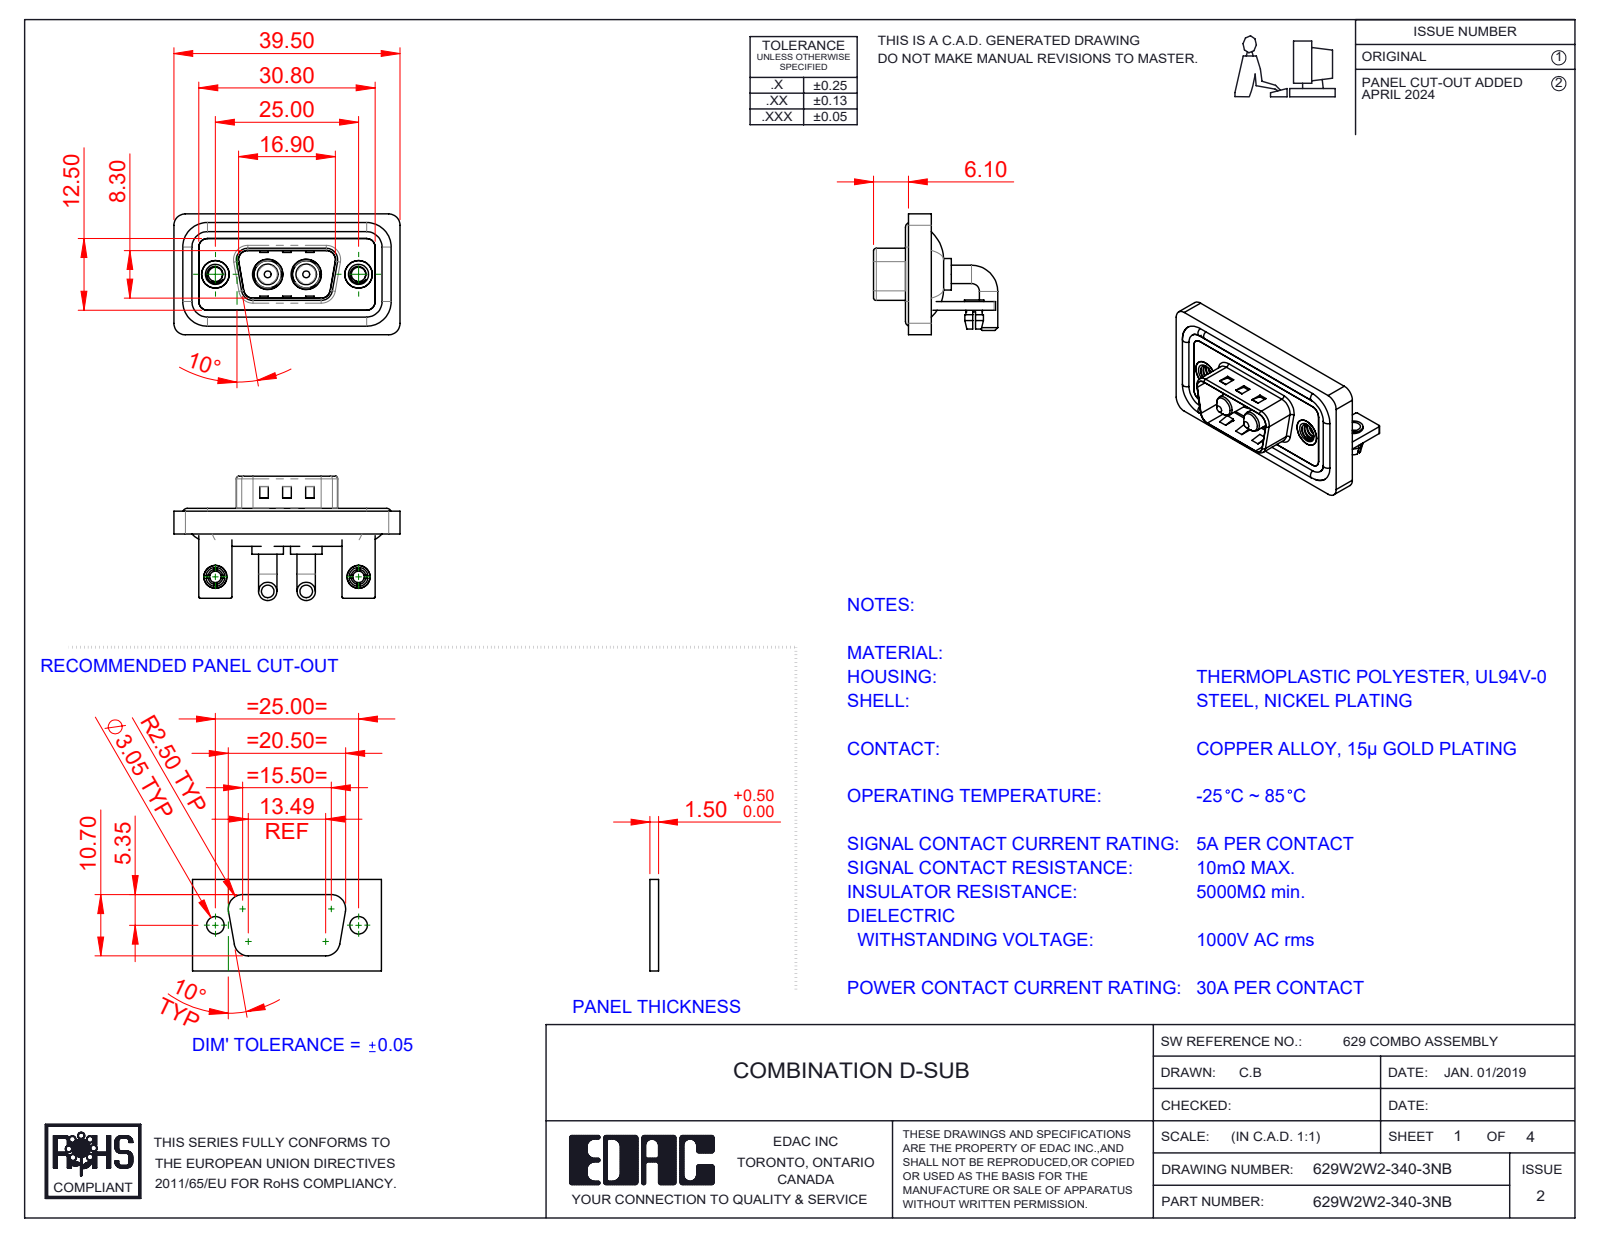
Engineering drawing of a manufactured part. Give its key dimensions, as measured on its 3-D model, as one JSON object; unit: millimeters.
{"part_name": "Power Pin_30A RA; 629Combo Waterproof Housing_09 Contacts; 629Combo Housing_2W2; 629Combo Shell Front_09 Contacts (+5 more)", "step_written_by": "SolidWorks 2023 (CONFIG_CONTROL_DESIGN)", "units": "millimeters", "bodies": {"solids": 15, "faces": 627, "planar": 233, "cylindrical": 272, "other": 122}, "overall_size": [39.5, 21.7, 21.1], "volume_mm3": 4949, "surface_area_mm2": 8003, "round_holes": [[2.5, 4], [2, 2], [3.2, 2], [4, 2], [4.8, 2], [4.85, 2], [5, 2], [5.3, 2]], "round_bosses_or_shafts": [[3.2, 4], [1.6, 4], [5.5, 2], [5.2, 2], [4.9, 2], [4.75, 2], [4, 2], [3.75, 2]], "partial_cylinders_radius": [[2, 19], [1.5, 18], [0.25, 16], [0.5, 9], [1.6, 8], [0.6, 4], [0.65, 4], [0.9, 4]], "face_to_face_distances": [0.4, 1.5, 2.9, 0.8, 1.1, 1.2, 2.1, 1.6, 3.7, 2.5], "hole_center_spacings": [9.14, 15.86, 25, 6.72]}
